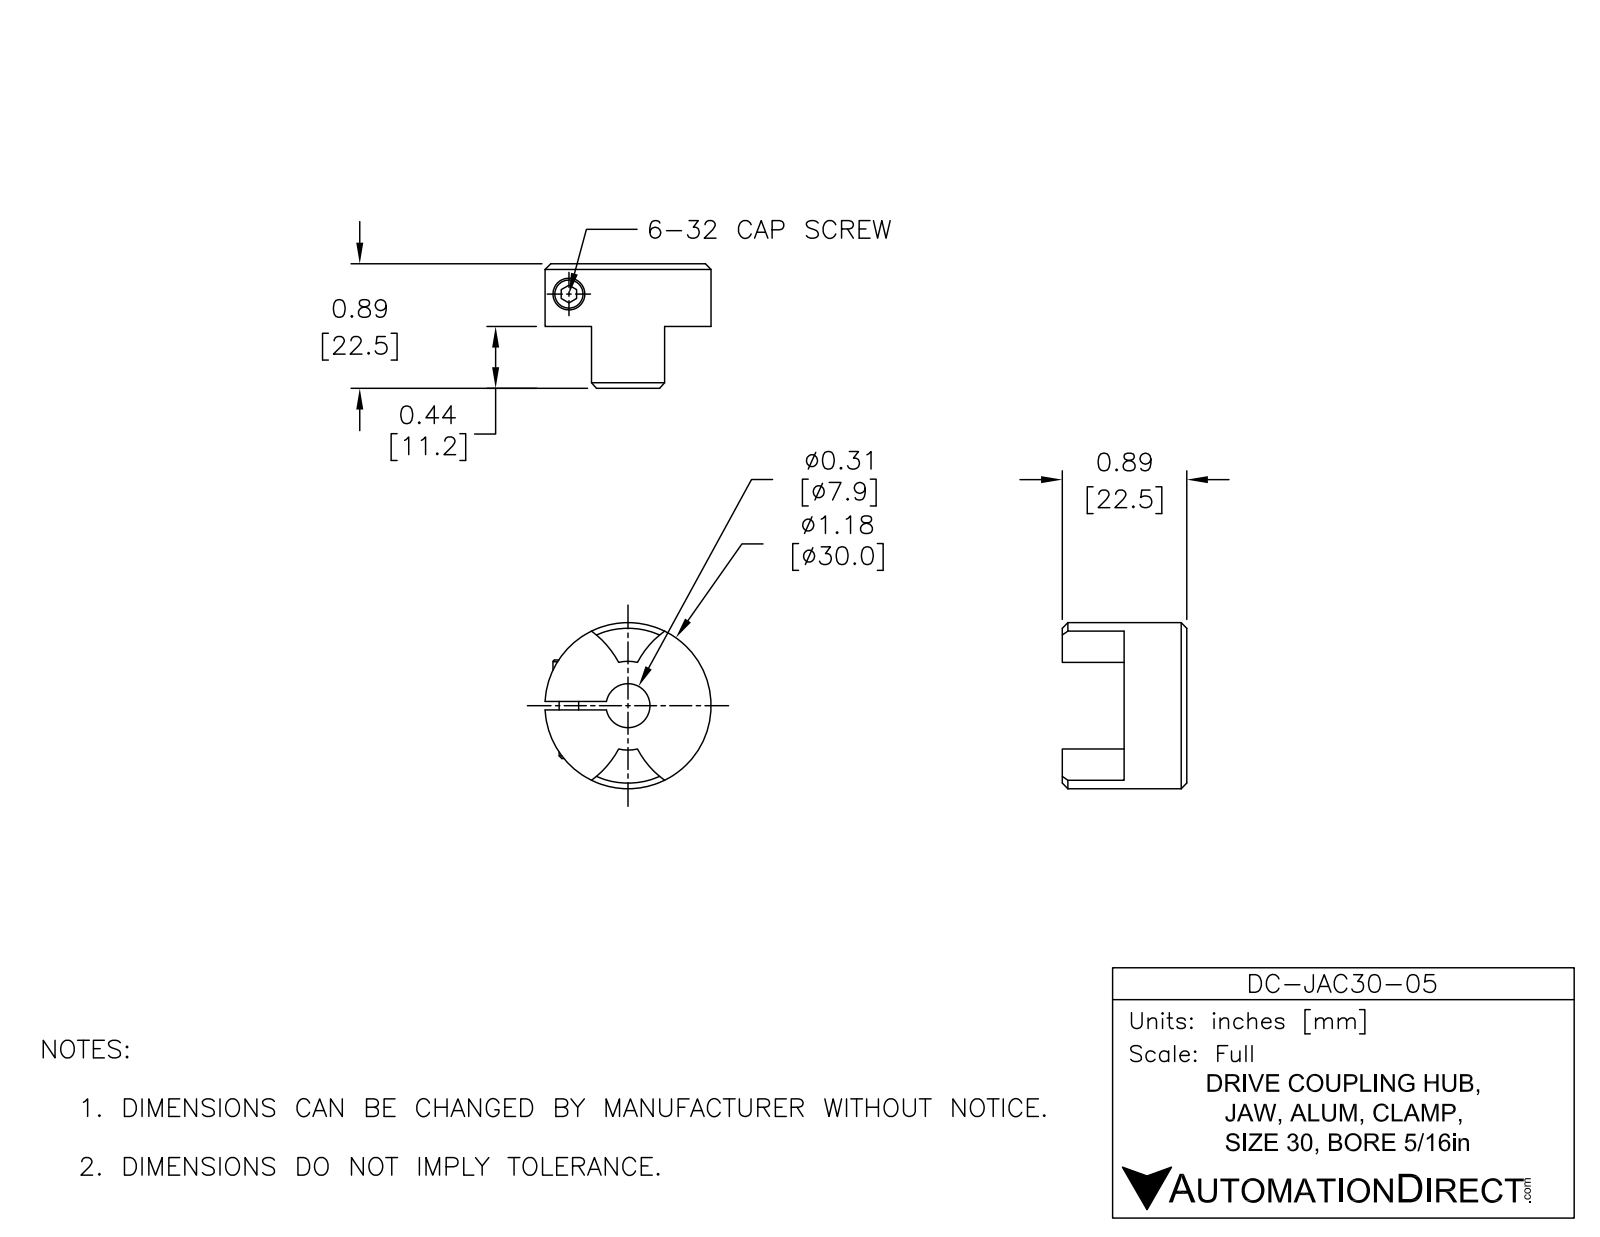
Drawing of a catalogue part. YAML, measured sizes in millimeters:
part_name: "DC-JAC30-05"
step_written_by: "SolidWorks 2015 (AUTOMOTIVE_DESIGN)"
units: millimeters
bodies: {solids: 1, faces: 27, planar: 7, cylindrical: 16, other: 4}
overall_size: [29.97, 29.95, 22.48]
volume: 8072
surface_area: 3683
round_holes:
  - {diameter: 3.91, count: 1}
  - {diameter: 6.35, count: 1}
  - {diameter: 7.94, count: 1}
round_bosses_or_shafts:
  - {diameter: 29.97, count: 1}
partial_cylinders:
  - {radius: 16.64, count: 2}
  - {radius: 8, count: 1}
face_to_face_distances: [11.3, 1.52, 22.48, 11.18, 5.51, 3.99]
